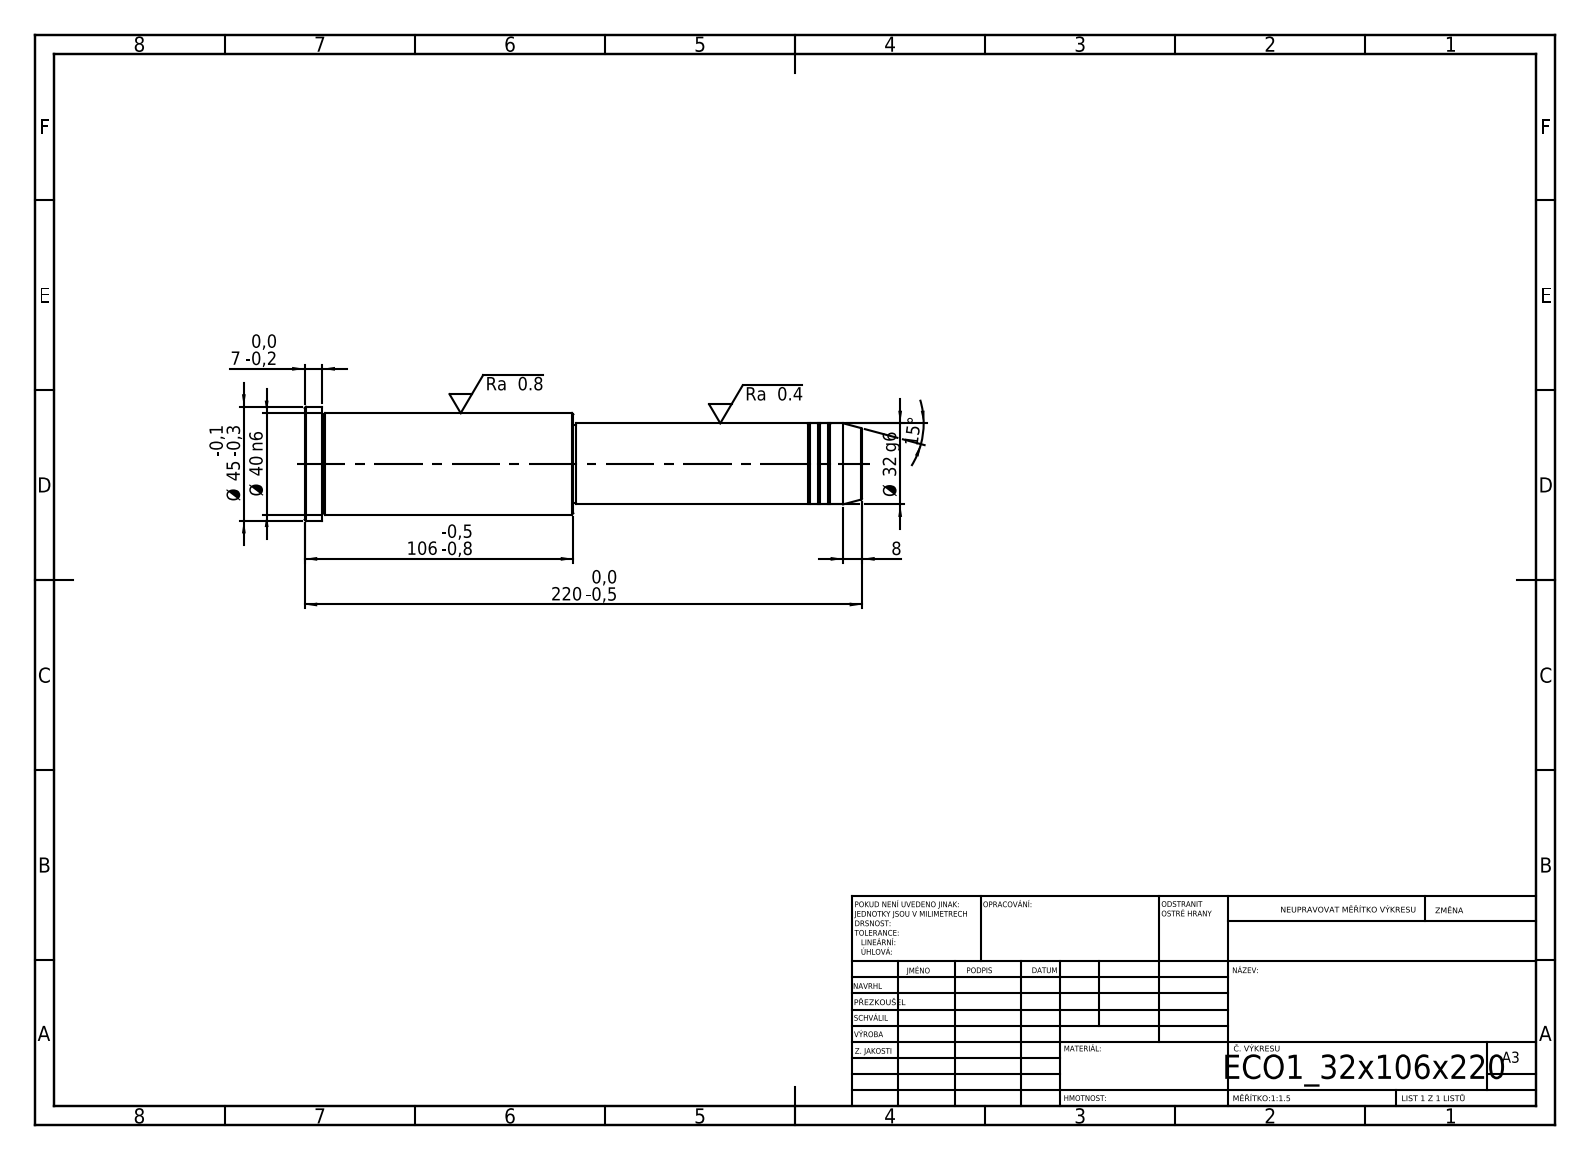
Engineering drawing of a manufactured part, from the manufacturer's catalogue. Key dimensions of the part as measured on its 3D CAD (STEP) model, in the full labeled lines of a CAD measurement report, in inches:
STEP written by: SolidWorks 2019 (CONFIG_CONTROL_DESIGN)
Units: inches
Bodies: 1 solid, 43 faces (5 planar, 14 cylindrical, 24 other)
Overall size (bounding box): 8.661 × 1.772 × 1.772
Volume: 13.81 in³ · Surface area: 43.55 in²
Round bosses / shafts (diameter × count): ⌀1.772 ×1, ⌀1.575 ×1, ⌀1.26 ×1, ⌀1.22 ×1
Main face-to-face distances: 8.661, 4.488, 4.173, 8.386, 3.898, 0.276, 4.449, 0.039, 3.937, 4.213
